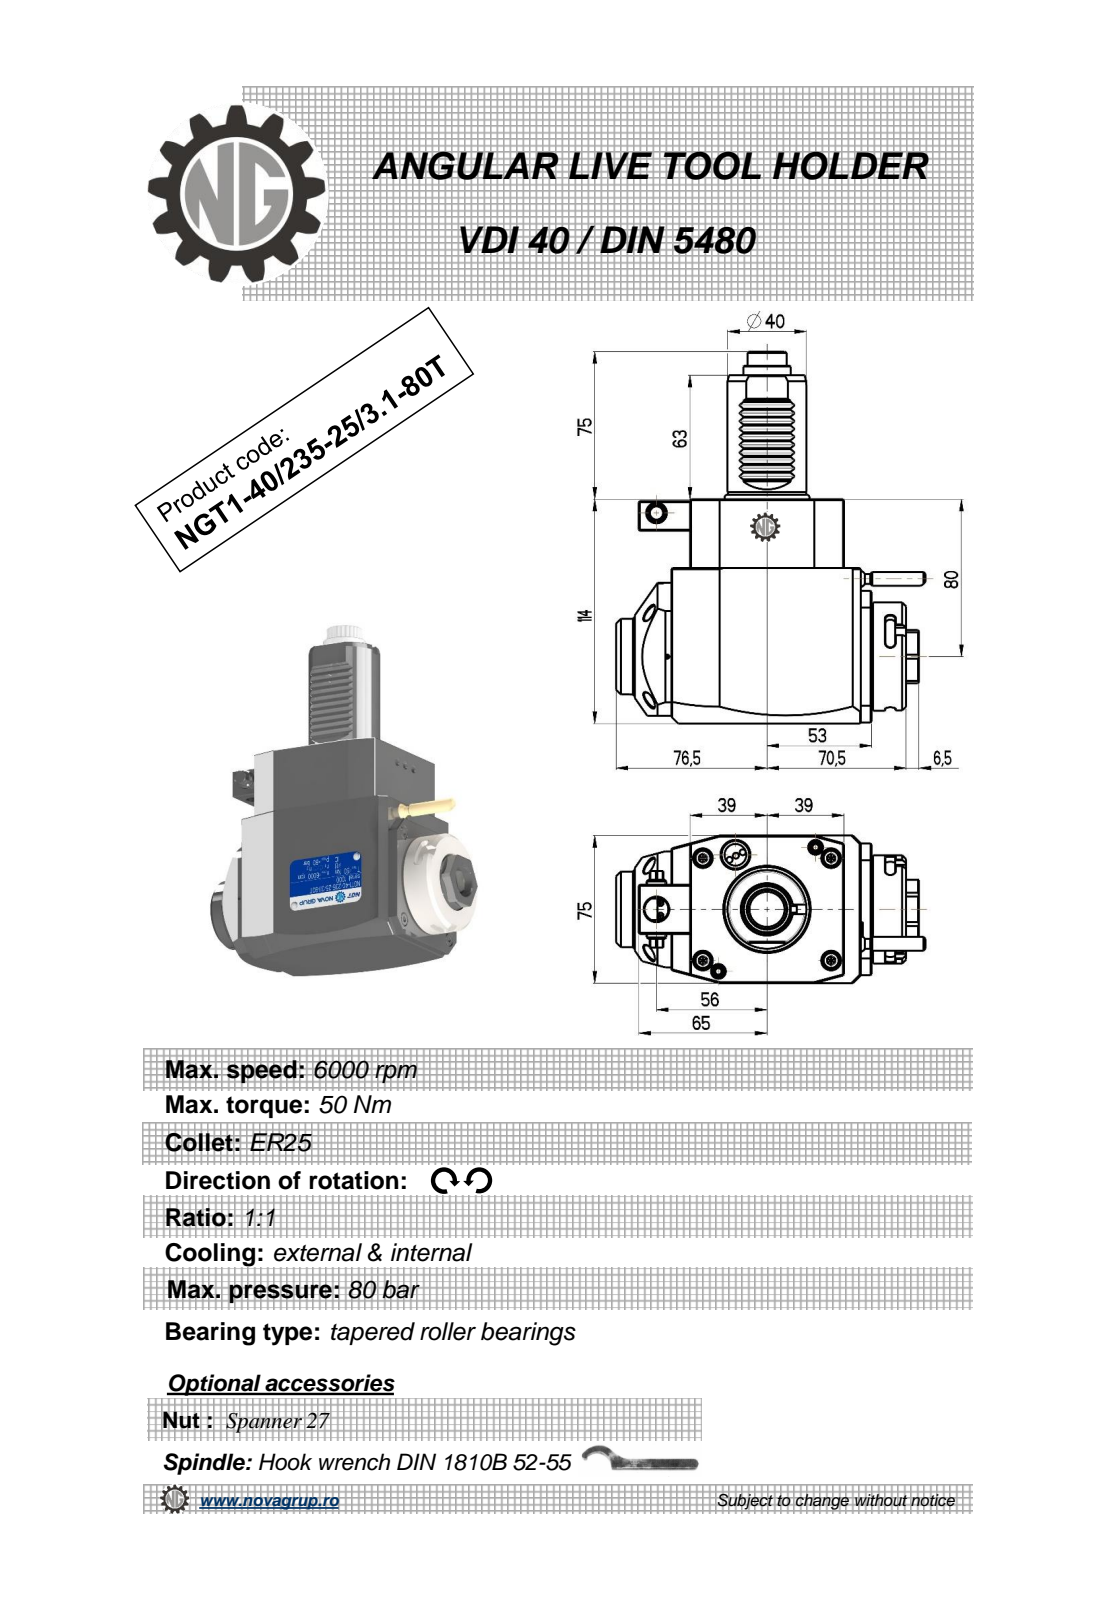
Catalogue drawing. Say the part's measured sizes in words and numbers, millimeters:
The part is named "NGT1_40_235_25_3_1_80T". Its 3-D file was written by "PRO/ENGINEER BY PARAMETRIC TECHNOLOGY CORPORATION, 2010280 (CONFIG_CONTROL_DESIGN)". It is 1 solid with 462 faces: 186 planar, 180 cylindrical and 96 other. Overall it measures 189 by 156.83 by 75 millimeters. Its volume is 970 598 cubic millimeters and its surface area 72 015 square millimeters. Round holes: 1 of diameter 2.5, 1 of diameter 3, 1 of diameter 9.5, 1 of diameter 12, 1 of diameter 18. Round bosses or shafts: 2 of diameter 8, 1 of diameter 55, 1 of diameter 48, 1 of diameter 40, 1 of diameter 38.5, 1 of diameter 24, 1 of diameter 10, 1 of diameter 7. Partial cylindrical surfaces (rounded edges, fillets, slot ends): 48 of radius 2.08, 10 of radius 0.3, 6 of radius 2.5, 2 of radius 15, 2 of radius 180, 1 of radius 3.85, 1 of radius 4.25, 1 of radius 9.08. The main face-to-face distances are 75, 114, 14, 109.5, 78, 92, 17.5, 31.5, 79, 35. The hole center spacings are 36.47, 43.2, 71.5.
